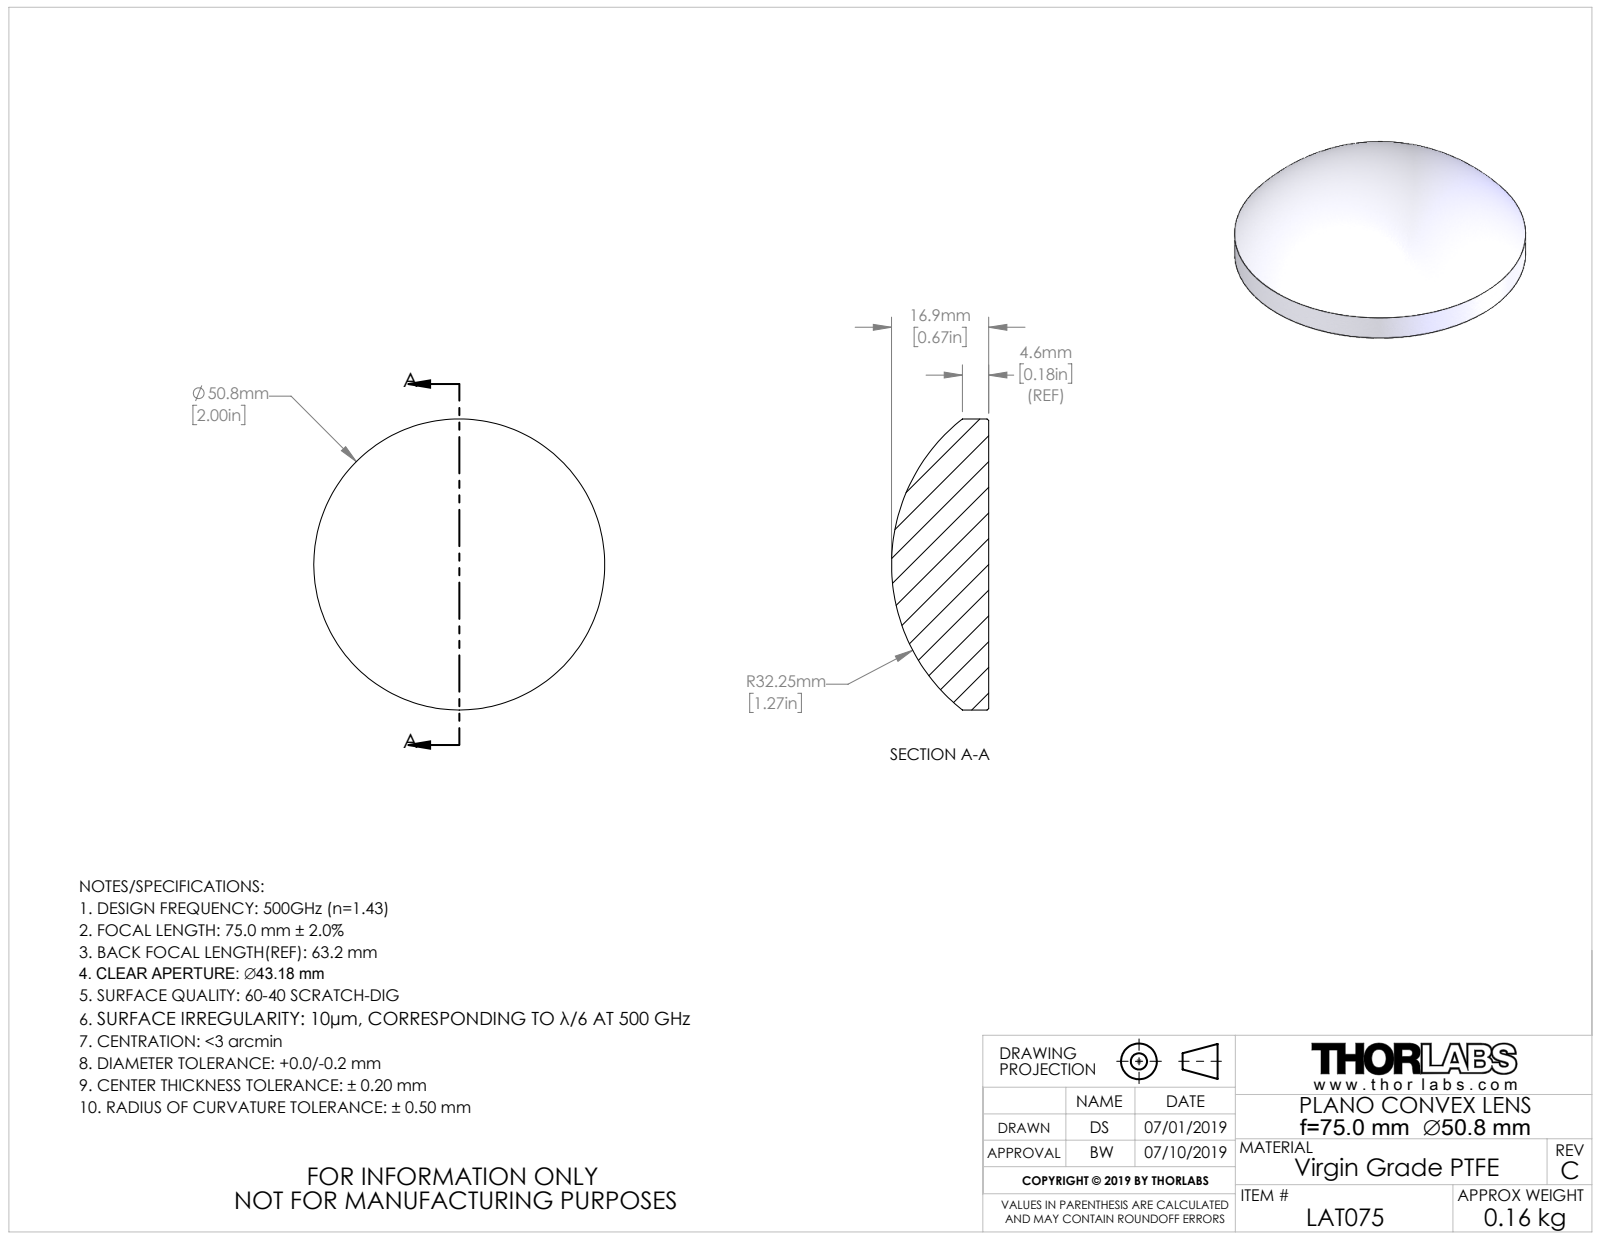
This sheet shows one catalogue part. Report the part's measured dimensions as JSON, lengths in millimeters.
{"part_name": "TTN041005-E0W", "step_written_by": "SolidWorks 2018 (CONFIG_CONTROL_DESIGN)", "units": "millimeters", "bodies": {"solids": 1, "faces": 7, "planar": 1, "cylindrical": 2, "other": 4}, "overall_size": [50.8, 50.8, 16.93], "volume_mm3": 22768, "surface_area_mm2": 5239, "round_bosses_or_shafts": [[50.8, 1]]}
